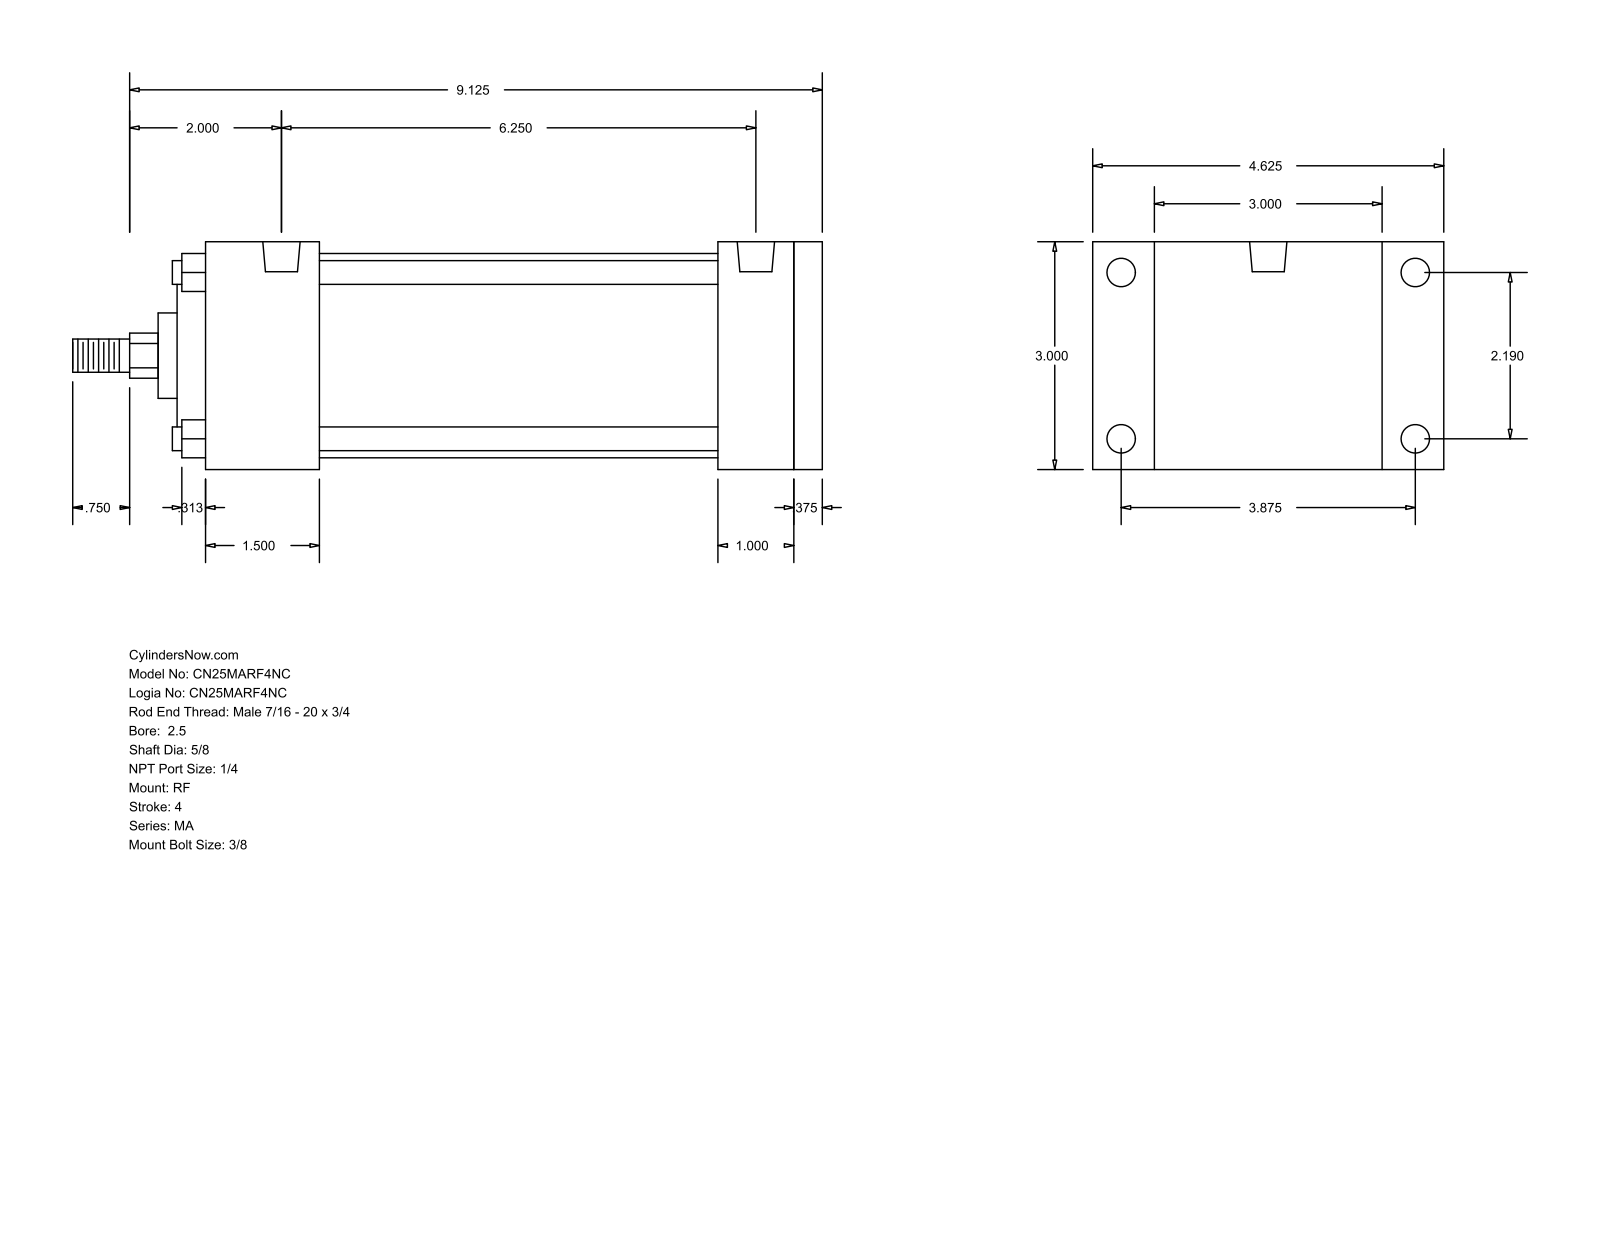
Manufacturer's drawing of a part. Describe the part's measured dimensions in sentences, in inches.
The part is named "MA_RF__0250_0.625". Its 3-D file was written by "GSSL Pune (CONFIG_CONTROL_DESIGN)". It is 0 solids with 94 faces: 65 planar, 29 cylindrical and 0 other. Overall it measures 9.875 by 4.625 by 3 inches. Round holes: 4 of diameter 0.313, 4 of diameter 0.375, 2 of diameter 0.492. Round bosses or shafts: 4 of diameter 0.313, 1 of diameter 2.69, 1 of diameter 2, 1 of diameter 1.125, 1 of diameter 0.625, 1 of diameter 0.437. Partial cylindrical surfaces (rounded edges, fillets, slot ends): 1 of radius 0.297. The main face-to-face distances are 3, 8.125, 0.375, 7.75, 1, 1.375, 1.5, 6.75, 5.25, 6.25. The hole center spacings are 2.19, 3.875, 4.451, 6.25.
